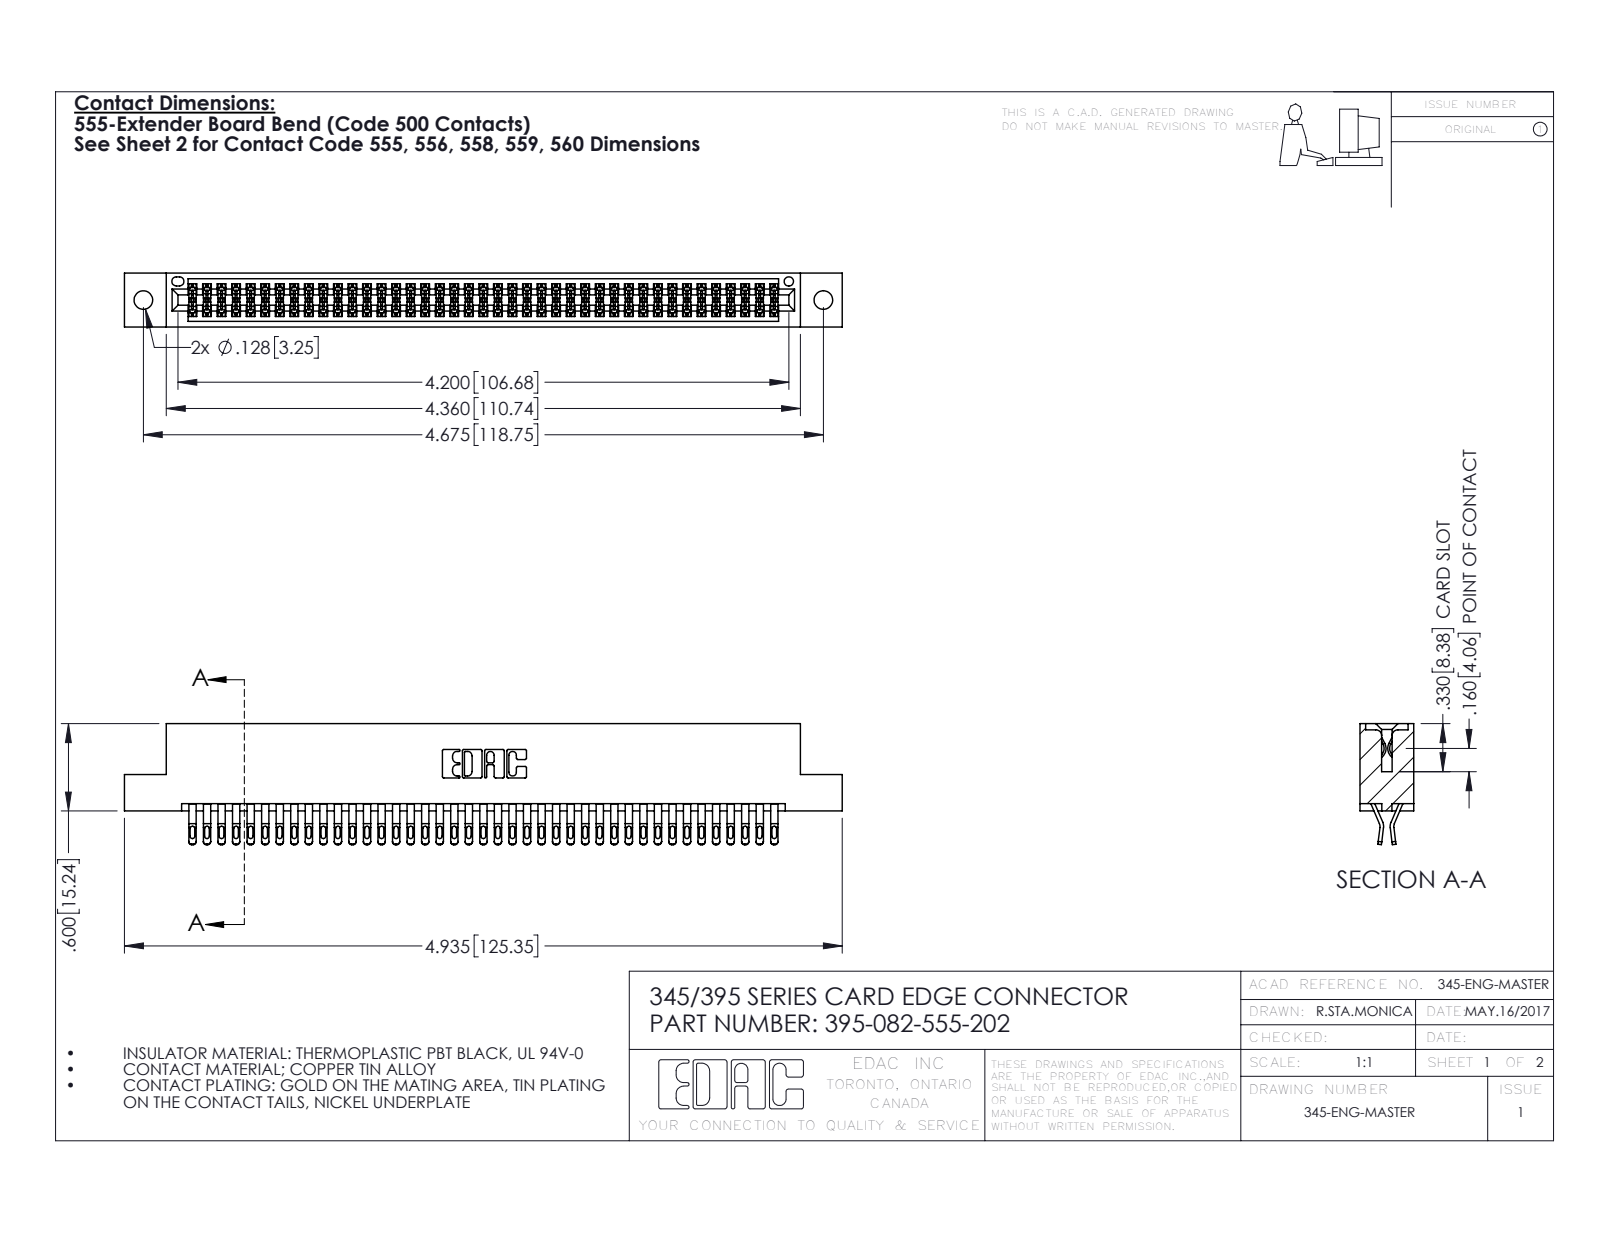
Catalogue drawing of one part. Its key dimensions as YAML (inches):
part_name: "345-292-001_555 Tail; 345 Part_Flush Mounting Lugs - 0.128 Dia; 395-082-555-202"
step_written_by: "SolidWorks 2016 (CONFIG_CONTROL_DESIGN)"
units: inches
bodies: {solids: 83, faces: 4718, planar: 2622, cylindrical: 2096, other: 0}
overall_size: [4.935, 0.832, 0.37]
volume: 0.755
surface_area: 29.17
round_holes:
  - {diameter: 0.128, count: 2}
  - {diameter: 0.064, count: 1}
partial_cylinders:
  - {radius: 0.016, count: 205}
  - {radius: 0.02, count: 164}
  - {radius: 0.006, count: 123}
  - {radius: 0.01, count: 22}
  - {radius: 0.007, count: 6}
  - {radius: 0.031, count: 6}
  - {radius: 0.026, count: 3}
  - {radius: 0.01, count: 2}
face_to_face_distances: [0.298, 0.072, 0.025, 0.37, 0.2, 0.098, 0.272, 0.225, 0.175, 0.149]
hole_center_spacings: [0.27, 4.439, 4.675]
